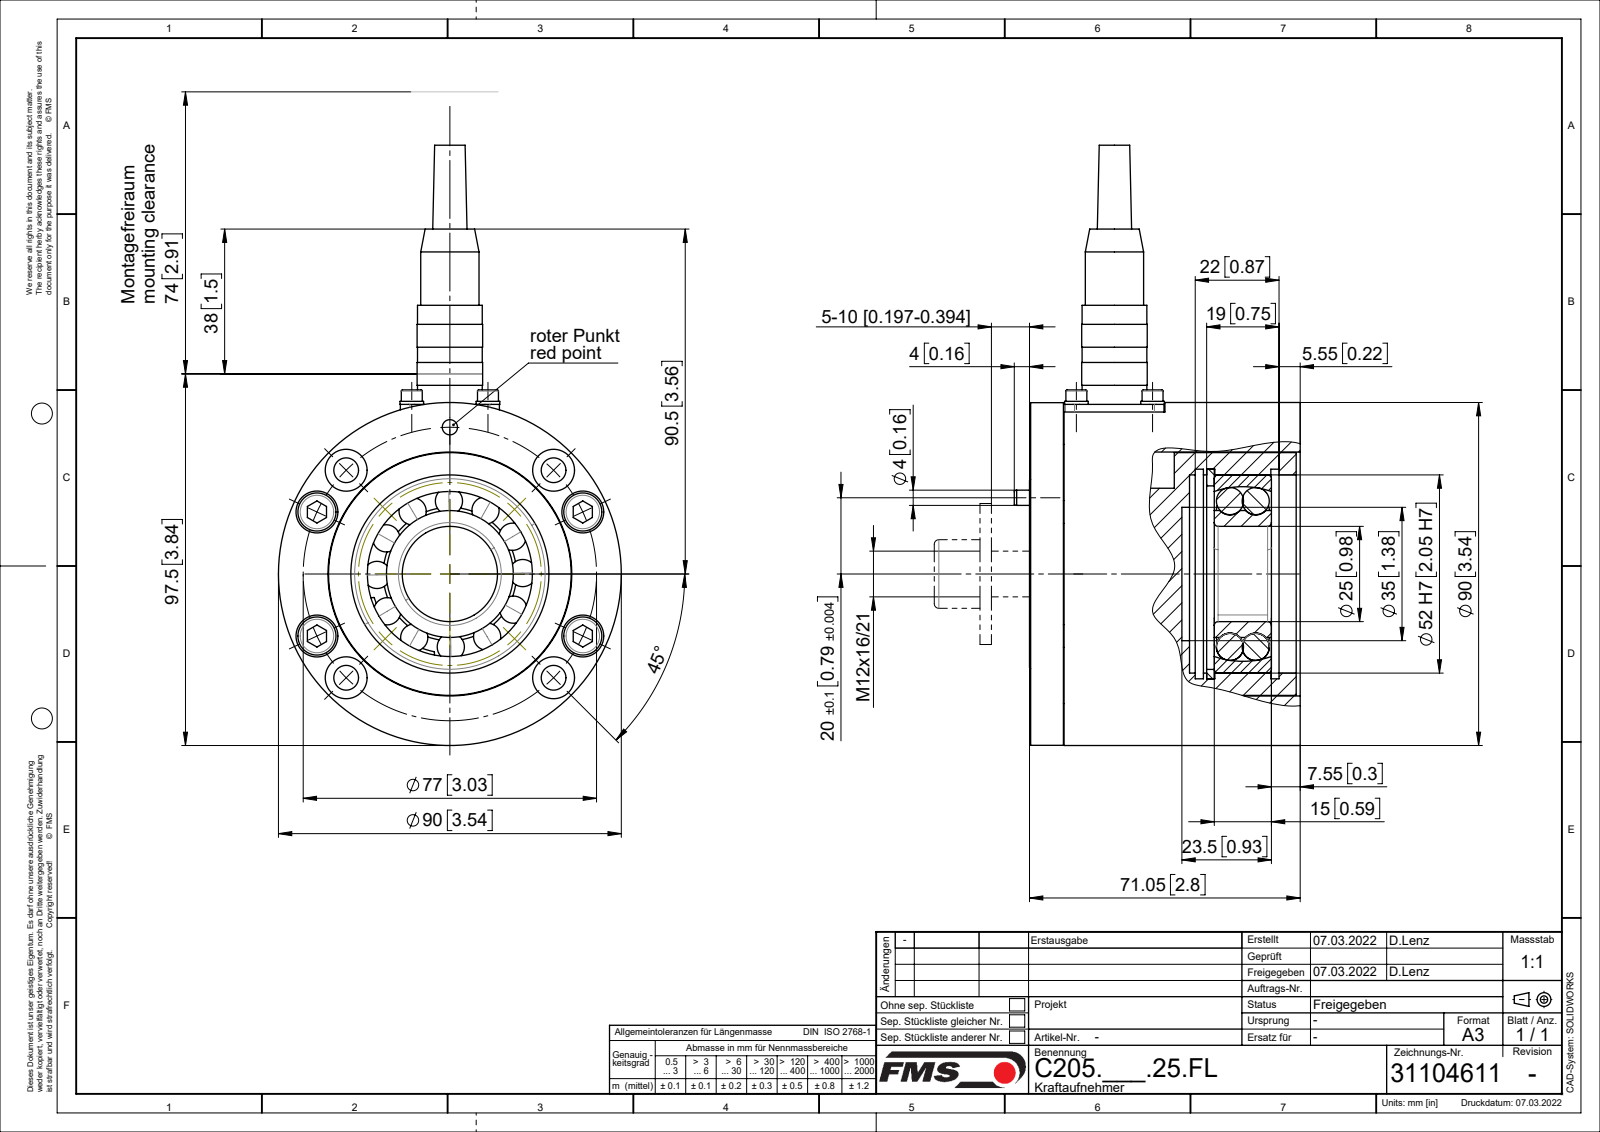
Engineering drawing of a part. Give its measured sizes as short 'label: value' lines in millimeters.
name: Flanschstecker_M14x1_Mini_5pol; Kabeldose_M14x1_Mini_5pol; Si-Ring DIN472_D52x2; PKL_1205_01 (+8 more)
written by: SolidWorks 2018 (CONFIG_CONTROL_DESIGN)
unit: mm
bodies: 47 solids, 599 faces (185 planar, 256 cylindrical, 158 other)
size: 157.5 × 96.05 × 90
volume: 318 683 mm³; area: 125 368 mm²
holes: 8× ⌀6.5, 8× ⌀11, 6× ⌀2.5, 4× ⌀3.1, 4× ⌀3.2, 4× ⌀5, 4× ⌀7, 2× ⌀4, 1× ⌀3, 1× ⌀10.2, 1× ⌀12, 1× ⌀13
bosses: 5× ⌀1.5, 4× ⌀10, 4× ⌀6.2, 4× ⌀6, 4× ⌀5.5, 4× ⌀3, 1× ⌀90, 1× ⌀89.9
rounds: 4× R0.1, 4× R2.5, 2× R0.5, 2× R4.24, 2× R5, 1× R20.8, 1× R24.1
face distances: 6, 2, 6.5, 32, 25.5, 33.05, 38, 8.6, 29.1, 37.7
hole spacings: 20, 38.5, 13.37, 14.14, 38.49, 44.16, 54.44, 63.07
